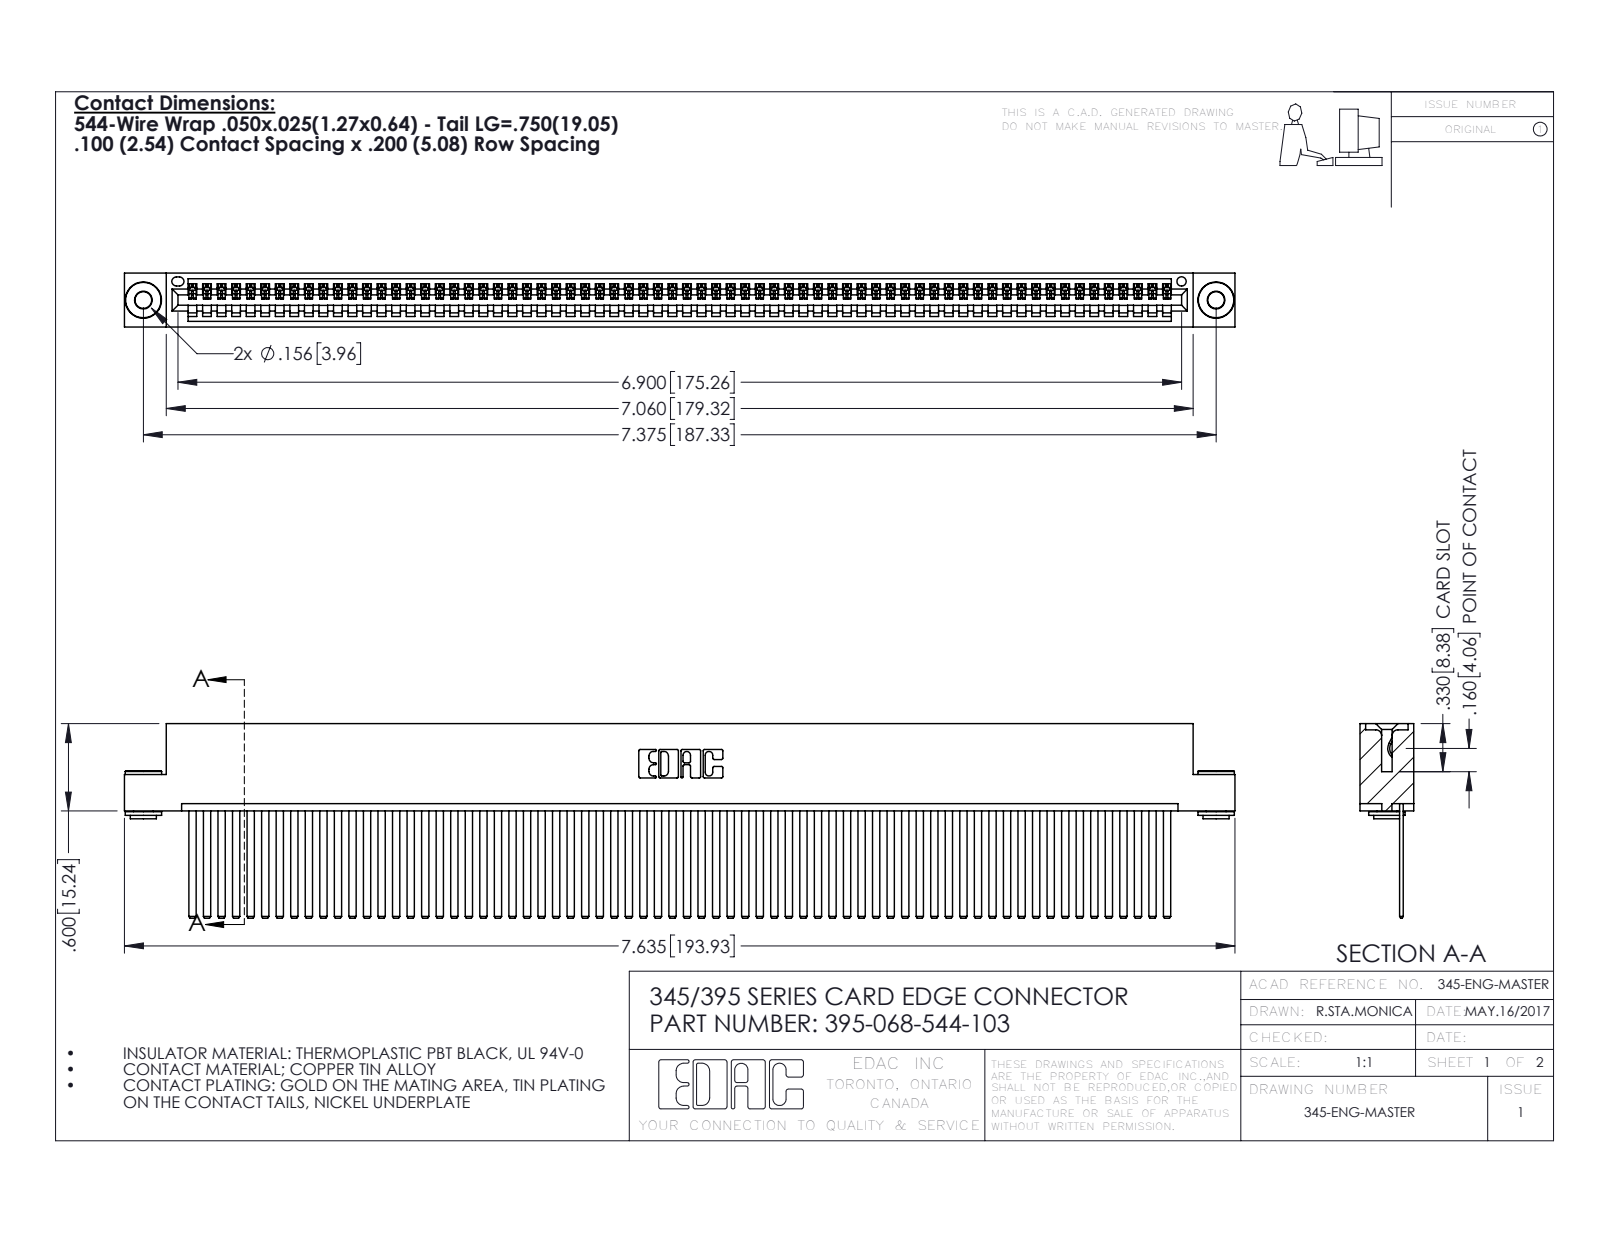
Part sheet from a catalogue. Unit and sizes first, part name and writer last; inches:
Units: inches
Overall size (bounding box): 7.635 × 1.337 × 0.37
Round holes (diameter × count): ⌀0.116 ×2, ⌀0.156 ×2, ⌀0.064 ×1
Round bosses / shafts (diameter × count): ⌀0.25 ×2, ⌀0.18 ×2, ⌀0.136 ×2
Partial cylindrical surfaces — rounded edges, fillets, slot ends (radius × count): R0.006 ×136, R0.01 ×22, R0.007 ×6, R0.031 ×6, R0.026 ×3, R0.031 ×2, R0.04 ×2, R0.014 ×1
Main face-to-face distances: 0.072, 0.298, 0.025, 0.098, 0.272, 0.37, 0.2, 0.225, 0.149, 0.072
Hole centre spacings: 0.27, 7.139, 7.375
Volume: 1.186 in³ · Surface area: 44.59 in²
Bodies: 71 solids, 3700 faces (2538 planar, 1154 cylindrical, 8 other)
Part name (STEP PRODUCT): 345-292-001_345-293-144; 345-250-002_345-250-002-102; 395-068-544-103; 345 Part_Flush Mounting Lugs - 0.156 Dia-TH
STEP written by: SolidWorks 2016 (CONFIG_CONTROL_DESIGN)
